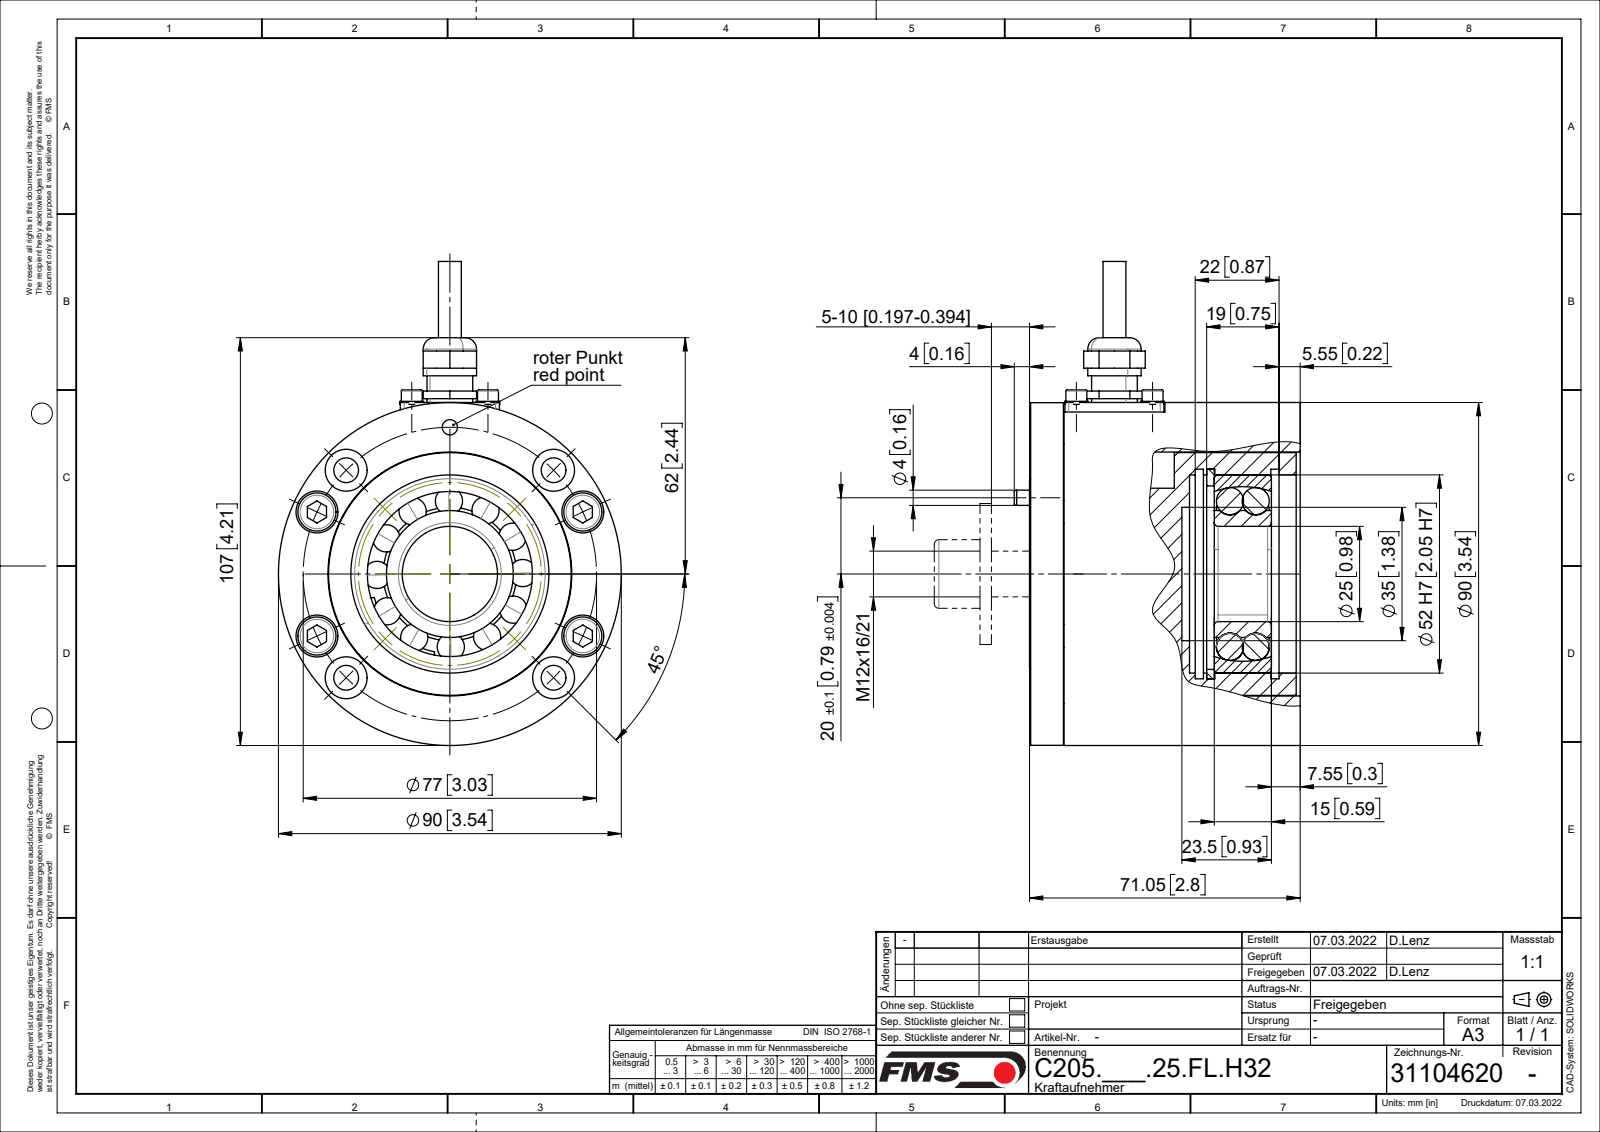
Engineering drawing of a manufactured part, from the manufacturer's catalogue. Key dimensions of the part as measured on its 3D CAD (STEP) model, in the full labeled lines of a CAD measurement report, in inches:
Part name (STEP PRODUCT): 31104488_01; 31104484_Stp_01; Federringe_DIN127A_M03; Zyl-Schr DIN912_M6x30 (+8 more)
STEP written by: SolidWorks 2018 (CONFIG_CONTROL_DESIGN)
Units: inches
Bodies: 48 solids, 577 faces (201 planar, 230 cylindrical, 146 other)
Overall size (bounding box): 5 × 3.781 × 3.543
Volume: 18.93 in³ · Surface area: 190.6 in²
Round holes (diameter × count): ⌀0.256 ×8, ⌀0.433 ×8, ⌀0.098 ×6, ⌀0.122 ×4, ⌀0.134 ×4, ⌀0.197 ×4, ⌀0.276 ×4, ⌀0.157 ×2, ⌀0.118 ×1, ⌀0.236 ×1, ⌀0.402 ×1, ⌀0.48 ×1
Round bosses / shafts (diameter × count): ⌀0.394 ×4, ⌀0.244 ×4, ⌀0.236 ×4, ⌀0.217 ×4, ⌀0.118 ×4, ⌀0.472 ×2, ⌀3.543 ×1, ⌀3.539 ×1
Partial cylindrical surfaces — rounded edges, fillets, slot ends (radius × count): R0.004 ×4, R0.039 ×4, R0.02 ×2, R0.167 ×2, R0.197 ×2, R0.819 ×1, R0.949 ×1
Main face-to-face distances: 0.236, 0.256, 1.26, 1.004, 0.079, 1.301, 1.496, 0.339, 1.146, 1.484
Hole centre spacings: 0.787, 1.516, 0.526, 0.557, 1.515, 1.739, 2.143, 2.483
